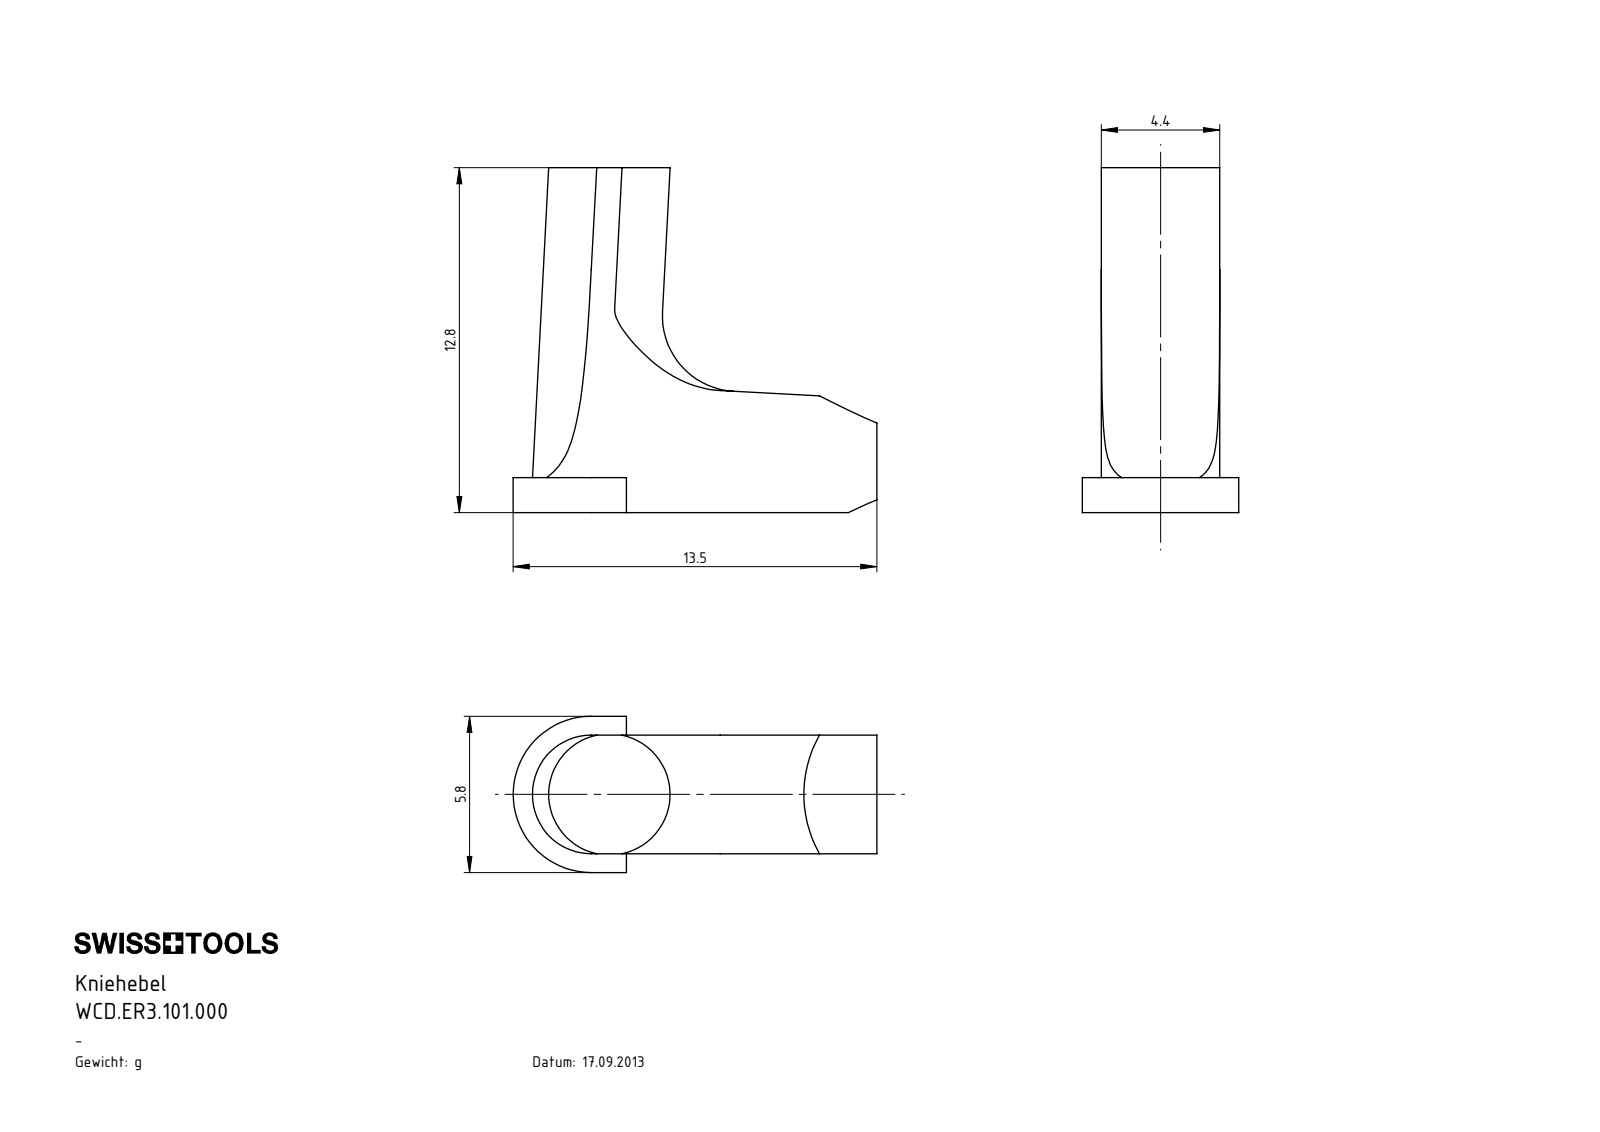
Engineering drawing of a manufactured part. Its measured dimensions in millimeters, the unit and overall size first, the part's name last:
Units: millimetres
Overall size (bounding box): 13.5 × 12.8 × 5.8
Round bosses / shafts (diameter × count): ⌀4.5 ×1
Partial cylindrical surfaces — rounded edges, fillets, slot ends (radius × count): R2.2 ×1, R2.9 ×1
Main face-to-face distances: 4.4, 12.8, 1.3, 11.5, 0.7, 5.1, 9.3, 5.8
Volume: 381 mm³ · Surface area: 377 mm²
Bodies: 1 solid, 22 faces (11 planar, 6 cylindrical, 5 other)
Part name (STEP PRODUCT): WCD.ER3.101.000
STEP written by: SolidWorks 2017 (AUTOMOTIVE_DESIGN)
